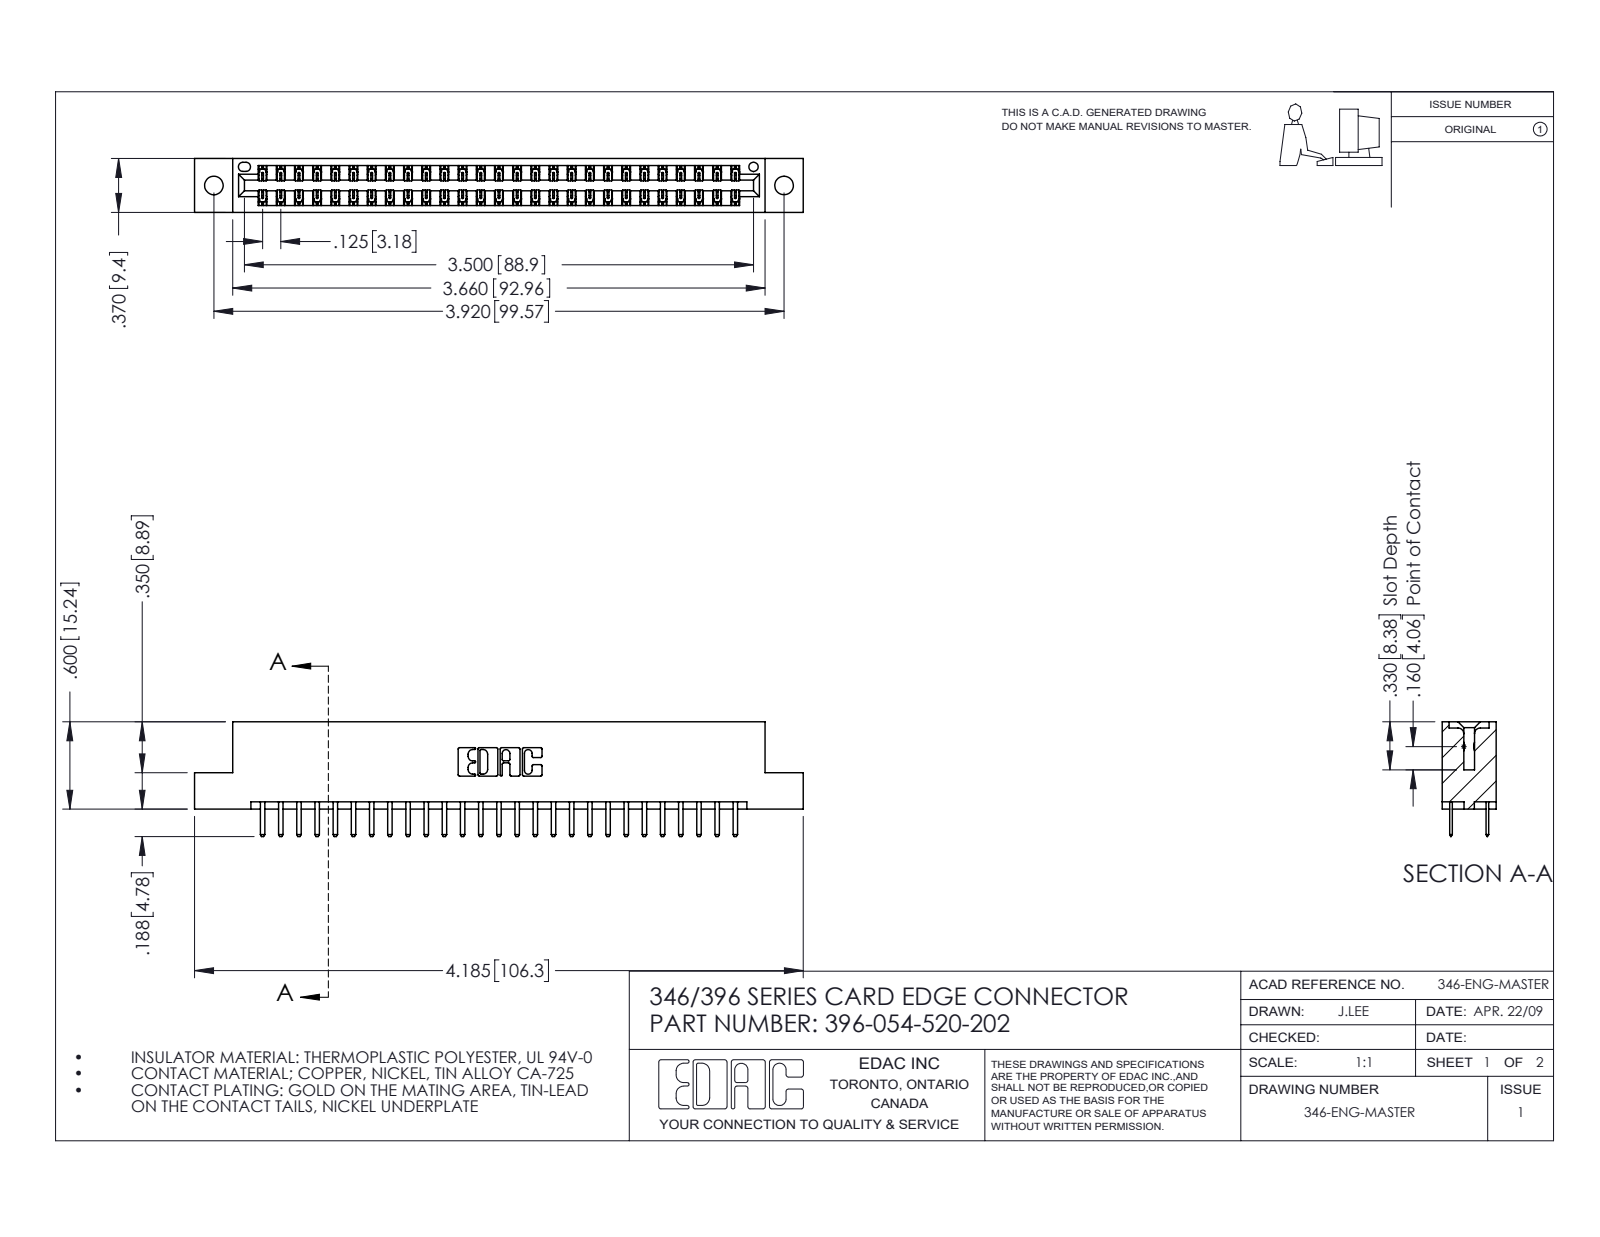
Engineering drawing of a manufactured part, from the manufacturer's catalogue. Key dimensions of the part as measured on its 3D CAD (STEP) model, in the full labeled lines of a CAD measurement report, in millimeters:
Part name (STEP PRODUCT): 345-292-001_345-293-120; 396-054-520-202; 346 Part_Flush Mounting Lugs - 0.128 Dia
STEP written by: SolidWorks 2016 (CONFIG_CONTROL_DESIGN)
Units: millimetres
Bodies: 55 solids, 3146 faces (2074 planar, 1072 cylindrical, 0 other)
Overall size (bounding box): 106.3 × 20 × 9.4
Volume: 10 200 mm³ · Surface area: 13 450 mm²
Round holes (diameter × count): ⌀3.3 ×2, ⌀1.6 ×1
Partial cylindrical surfaces — rounded edges, fillets, slot ends (radius × count): R0.2 ×81, R0.3 ×58, R0.3 ×22, R0.2 ×6, R0.8 ×6, R0.7 ×3, R0.4 ×2, R0.6 ×2
Main face-to-face distances: 1.2, 8.2, 6.4, 9.4, 7, 1.8, 7.6, 0.6, 3.8, 5.6
Hole centre spacings: 6.2, 94.3, 99.6
